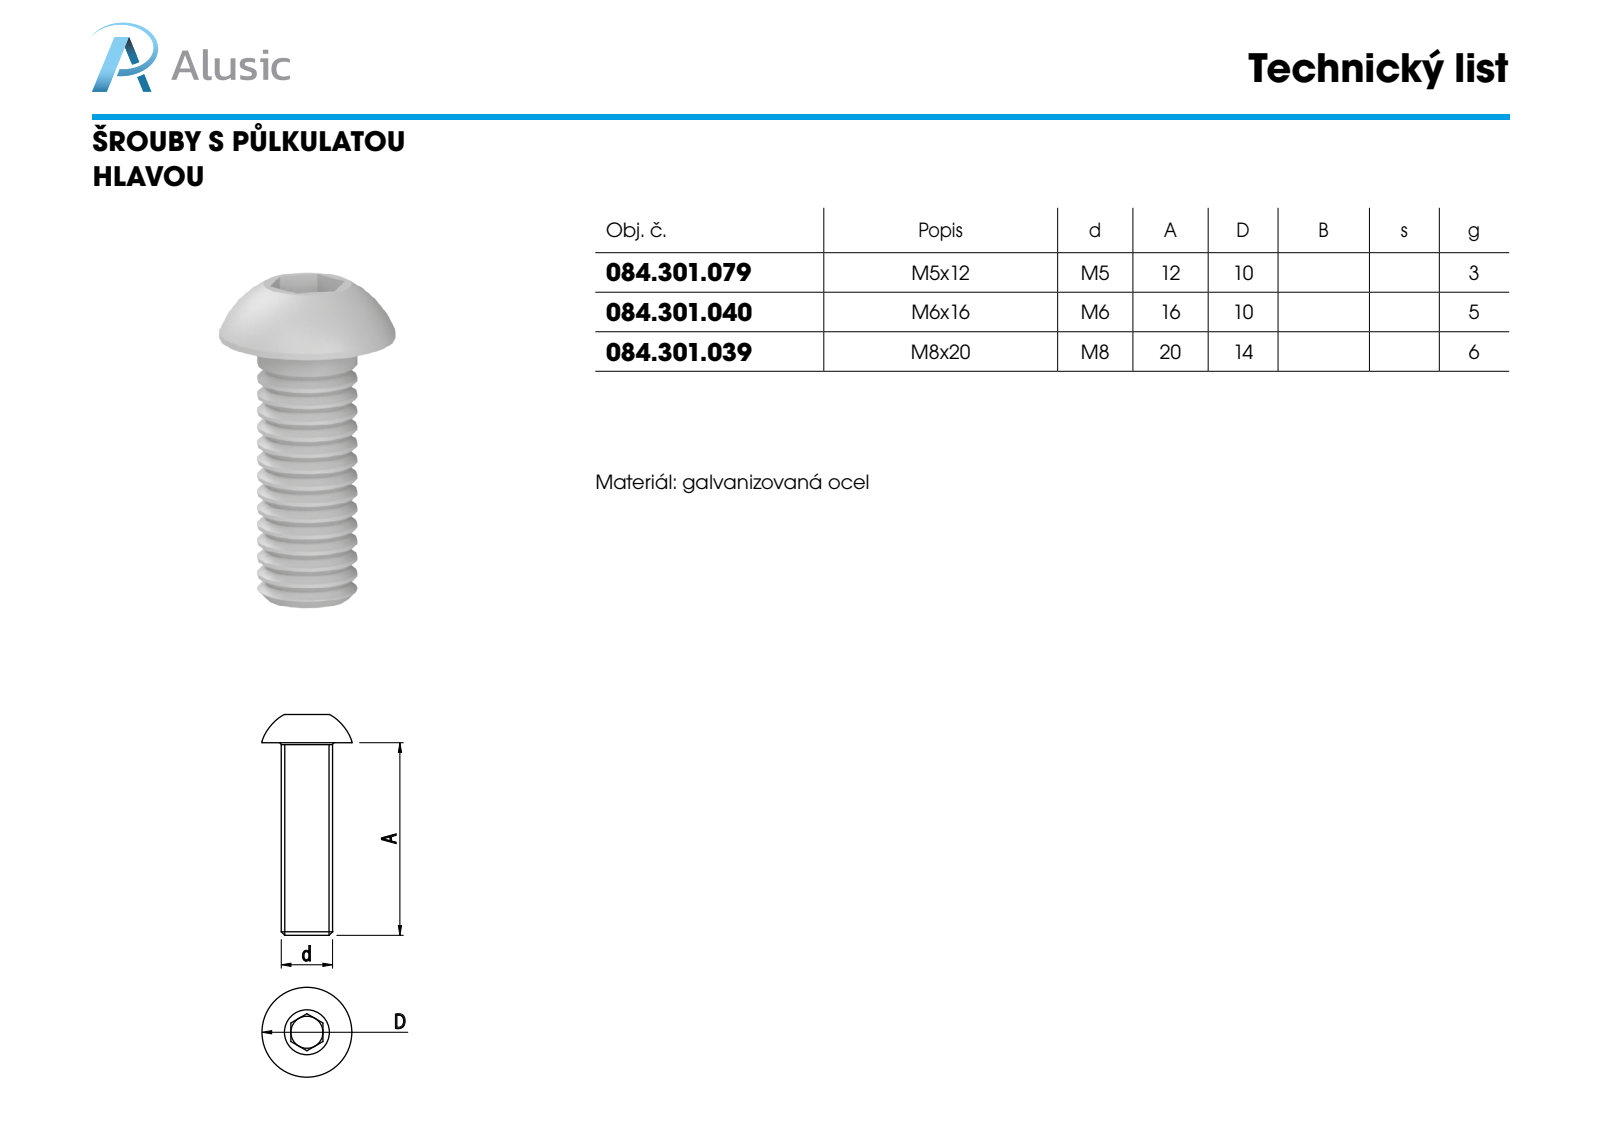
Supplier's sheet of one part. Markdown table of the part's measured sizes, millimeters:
| quantity | value |
| --- | --- |
| part name | socket button head screw_iso_ISO 7380 - M6 x 16 --- 16N; 084.301.040 |
| STEP written by | SolidWorks 2012 (CONFIG_CONTROL_DESIGN) |
| units | millimeters |
| bodies | 1 solid, 27 faces (15 planar, 4 cylindrical, 8 other) |
| overall size | 19.3 × 10.5 × 10.5 |
| volume | 620 mm³ |
| surface area | 548 mm² |
| round bosses / shafts (diameter × count) | 10.5 × 1, 6 × 1 |
| main face-to-face distances | 16, 4, 3.3, 19.3, 2.08, 1.22, 17.22 |
